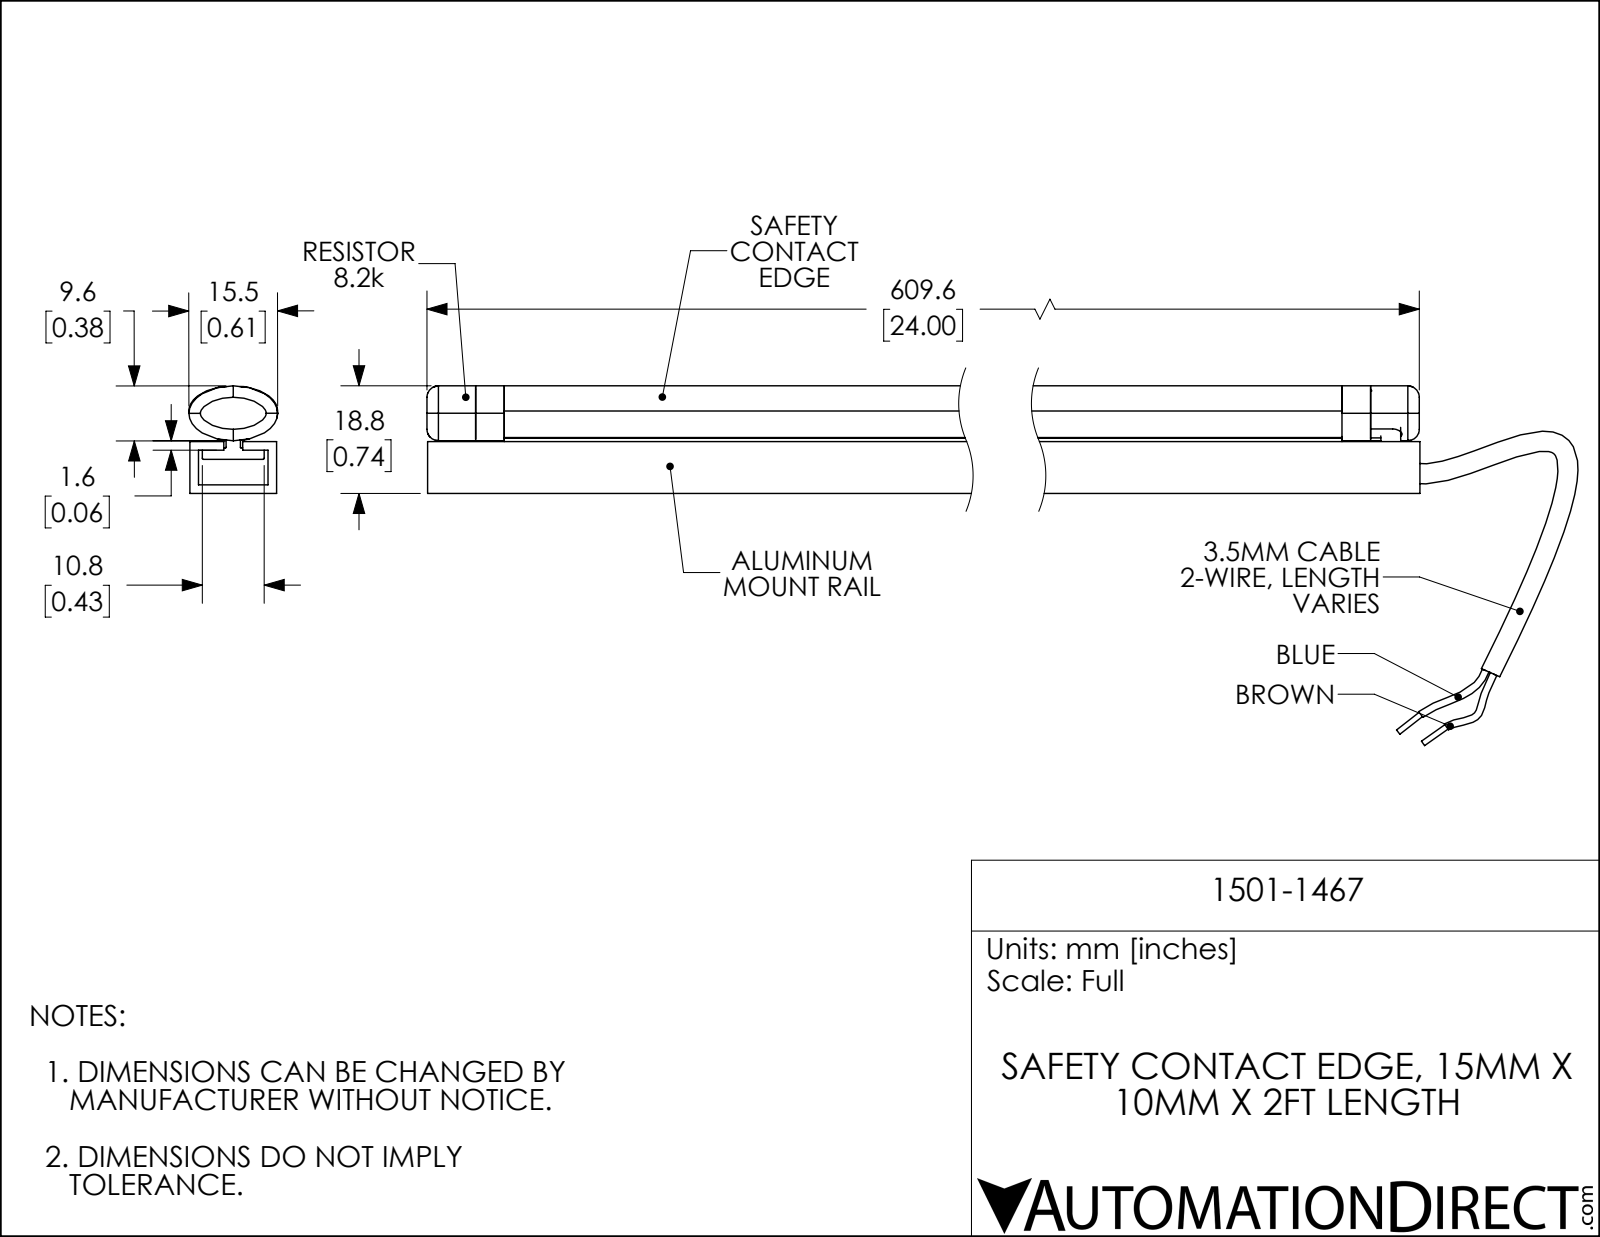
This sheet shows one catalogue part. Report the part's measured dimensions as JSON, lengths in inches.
{"part_name": "1501-1467", "step_written_by": "SolidWorks 2018 (AUTOMOTIVE_DESIGN)", "units": "inches", "bodies": {"solids": 7, "faces": 607, "planar": 129, "cylindrical": 154, "other": 324}, "overall_size": [25.091, 2.473, 0.611], "volume_in3": 5.959, "surface_area_in2": 170.2, "round_holes": [[0.047, 4]], "round_bosses_or_shafts": [[0.037, 2]], "partial_cylinders_radius": [[0.004, 52], [0.016, 15], [0.012, 10], [0.008, 7], [0.02, 4], [0.512, 4], [0.008, 3], [0.059, 3]], "face_to_face_distances": [0.059, 0.297, 0.537, 0.356, 0.016, 0.122, 0.234, 0.175, 0.596, 0.238], "hole_center_spacings": [0.197, 0.196, 0.197]}
